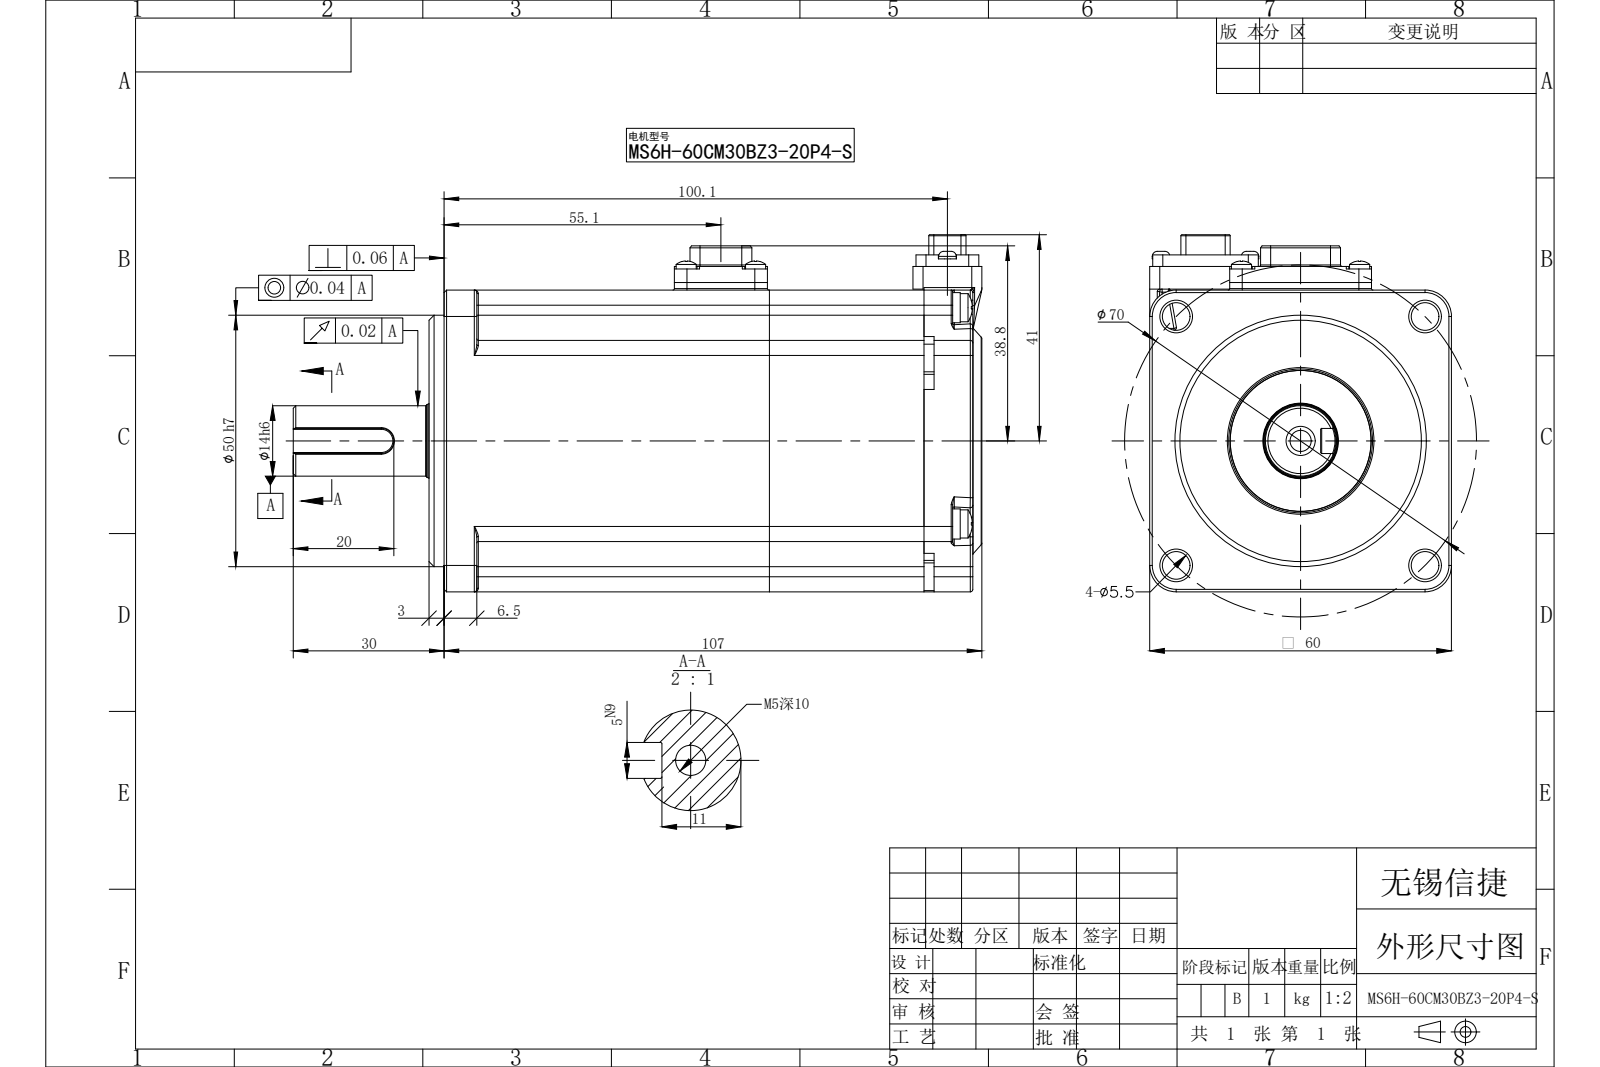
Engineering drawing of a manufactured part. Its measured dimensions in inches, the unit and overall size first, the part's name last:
Units: inches
Overall size (bounding box): 5.392 × 2.795 × 2.362
Round holes (diameter × count): ⌀0.083 ×4, ⌀0.217 ×4, ⌀0.063 ×2, ⌀0.165 ×1, ⌀0.591 ×1
Round bosses / shafts (diameter × count): ⌀0.236 ×4, ⌀0.22 ×4, ⌀0.217 ×4, ⌀0.157 ×4, ⌀0.138 ×2, ⌀1.969 ×1, ⌀1.102 ×1, ⌀0.583 ×1
Partial cylindrical surfaces — rounded edges, fillets, slot ends (radius × count): R0.02 ×38, R0.012 ×36, R0.008 ×20, R0.118 ×17, R0.079 ×16, R0.039 ×5, R0.098 ×5, R0.024 ×4
Main face-to-face distances: 2.362, 0.394, 1.969, 3.876, 0.453, 4.329, 0.118, 4.211, 3.758, 0.071
Hole centre spacings: 1.378, 1.949, 0.315, 0.654, 0.726, 2.756, 0.925, 1.617
Bodies: 0 solids, 807 faces (374 planar, 256 cylindrical, 177 other)
Part name (STEP PRODUCT): MS6H-60CM30BZ3-20P4-S
STEP written by: SolidWorks 2022 (CONFIG_CONTROL_DESIGN)
